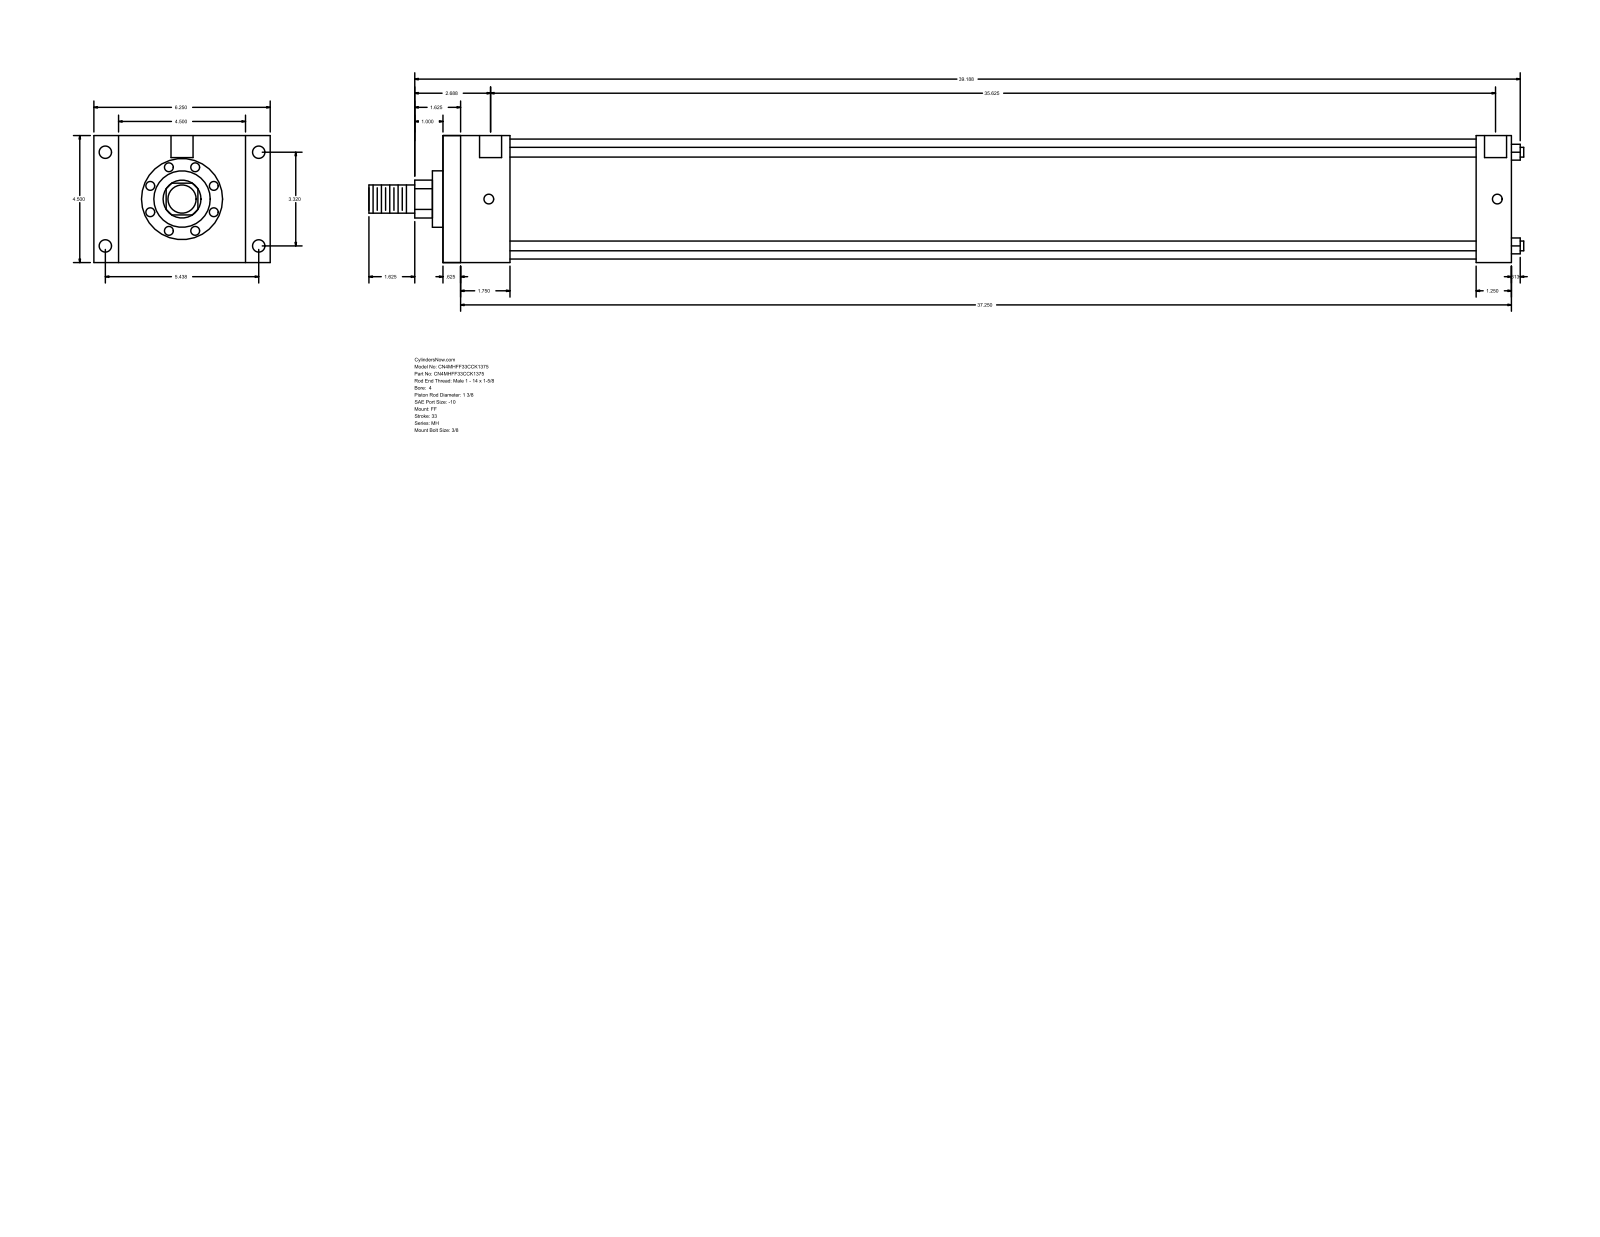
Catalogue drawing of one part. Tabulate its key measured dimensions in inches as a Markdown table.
| quantity | value |
| --- | --- |
| part name | MH_FF__0400_1.375 |
| STEP written by | GSSL Pune (CONFIG_CONTROL_DESIGN) |
| units | inches |
| bodies | 0 solids, 92 faces (64 planar, 28 cylindrical, 0 other) |
| overall size | 40.937 × 6.25 × 4.5 |
| round holes (diameter × count) | 0.344 × 4, 0.438 × 4, 0.781 × 2 |
| round bosses / shafts (diameter × count) | 0.345 × 4, 4.25 × 1, 2 × 1, 1.375 × 1, 1 × 1 |
| partial cylindrical surfaces (radius × count) | 0.672 × 1 |
| main face-to-face distances | 4.5, 37.875, 0.625, 37.25, 2.375, 1.75, 35.5, 36.625, 36, 34.25 |
| hole center spacings | 0.063, 3.32, 5.438, 6.371, 35.688, 35.75, 35.625 |
